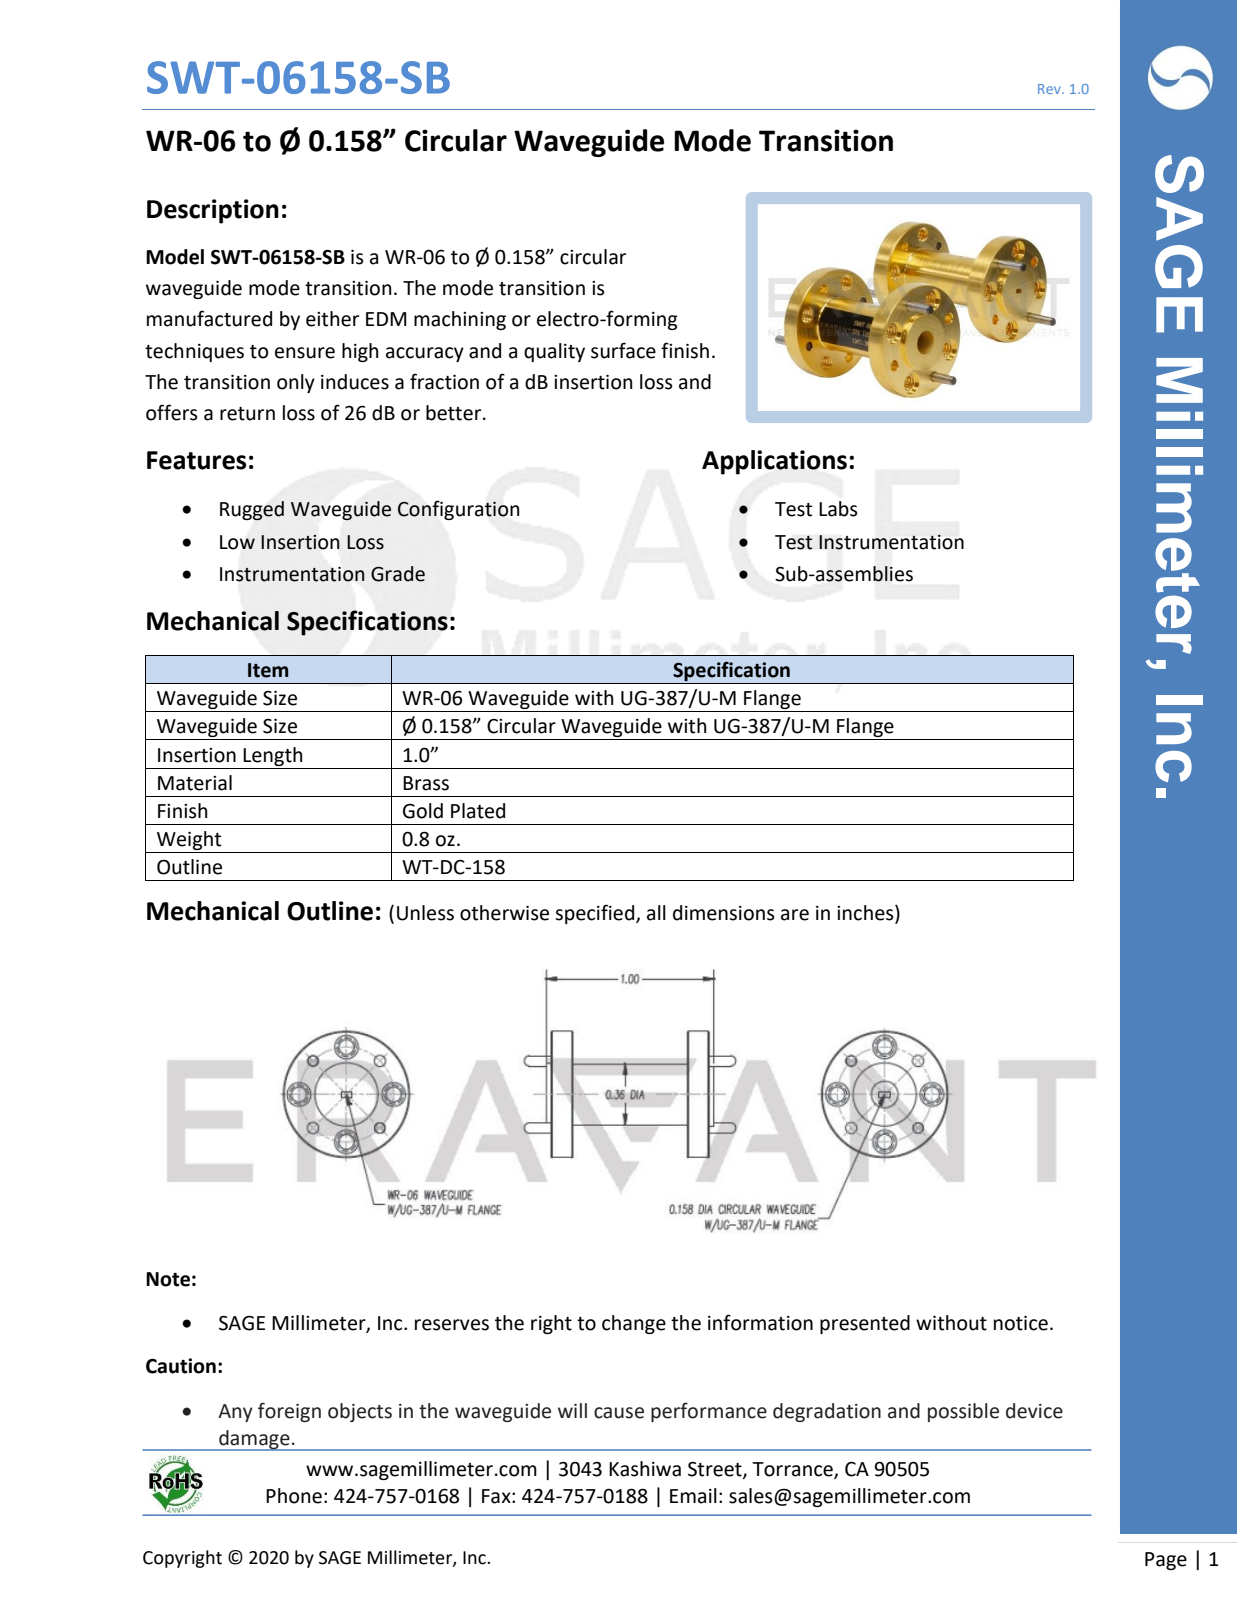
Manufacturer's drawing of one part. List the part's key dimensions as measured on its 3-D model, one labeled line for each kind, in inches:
Part name (STEP PRODUCT): WT-DC-158, Defeatured
STEP written by: SolidWorks 2021 (AUTOMOTIVE_DESIGN)
Units: inches
Bodies: 5 solids, 138 faces (24 planar, 66 cylindrical, 48 other)
Overall size (bounding box): 1.305 × 0.75 × 0.75
Volume: 0.183 in³ · Surface area: 3.599 in²
Round holes (diameter × count): ⌀0.06 ×4, ⌀0.067 ×4, ⌀0.089 ×4, ⌀0.14 ×4
Round bosses / shafts (diameter × count): ⌀0.063 ×4, ⌀0.75 ×1, ⌀0.375 ×1, ⌀0.36 ×1
Main face-to-face distances: 0.68, 0.94, 0.81, 0.13, 0.13, 0.81, 0.03, 0.97, 0.84, 0.16
Hole centre spacings: 0.215, 0.398, 0.519, 0.562, 0.52, 0.563
